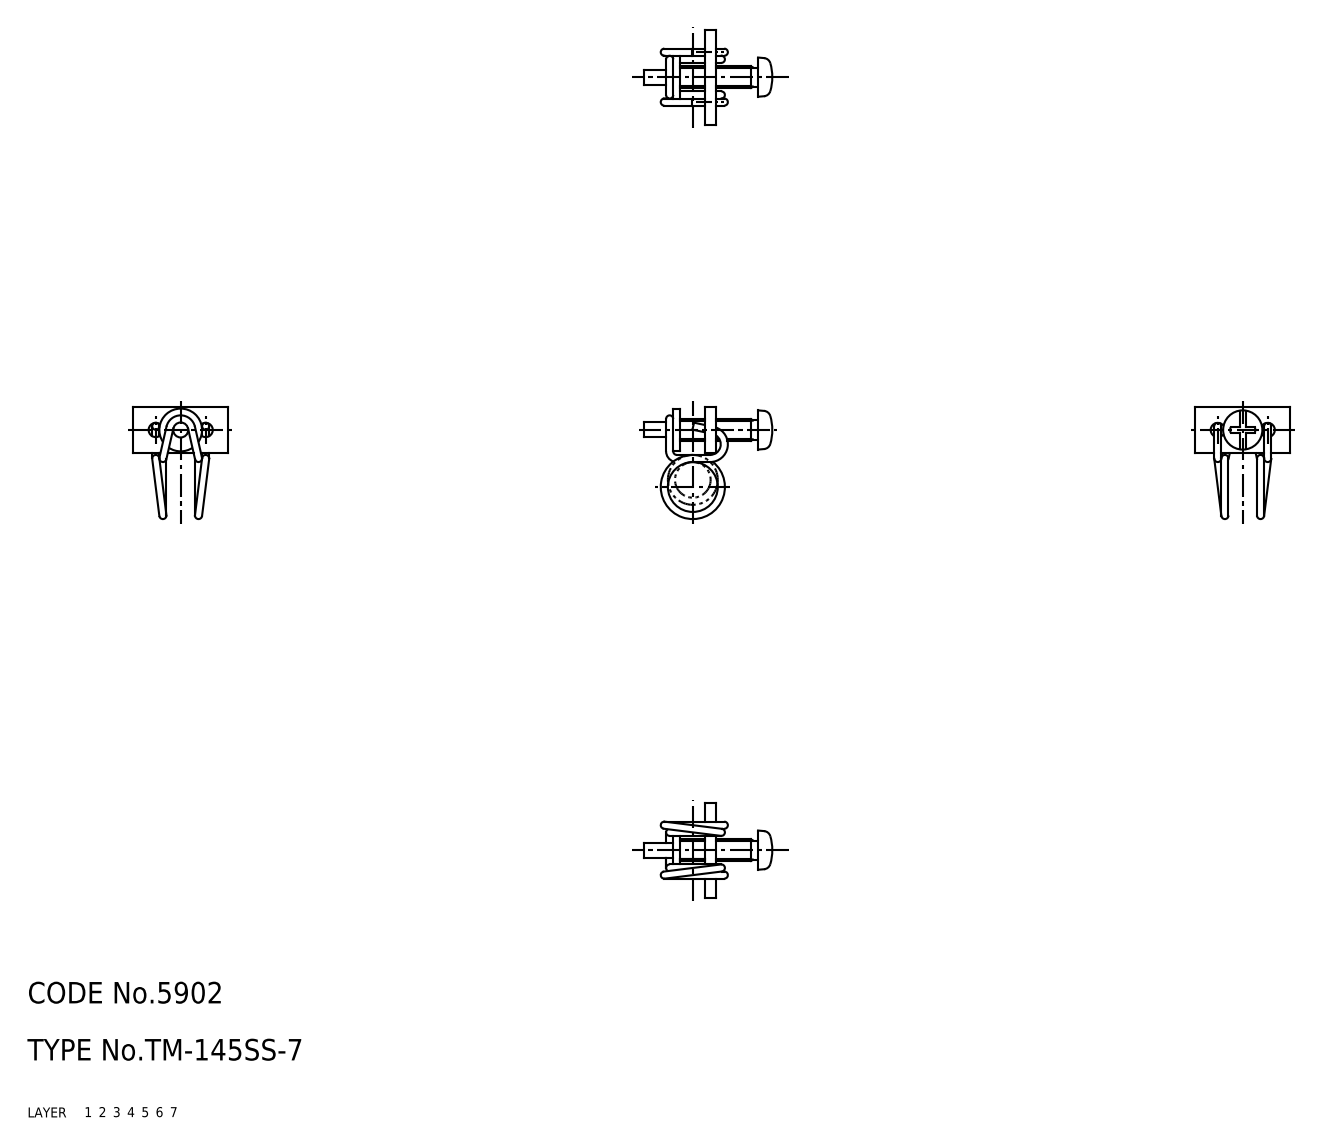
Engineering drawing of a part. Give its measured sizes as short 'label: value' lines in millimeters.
name: 67115249; 67115262; 67115275
written by: CADfix (AUTOMOTIVE_DESIGN)
unit: mm
bodies: 3 solids, 75 faces (0 planar, 0 cylindrical, 75 other)
size: 17.98 × 15.75 × 13.3
volume: 339 mm³; area: 805 mm²
